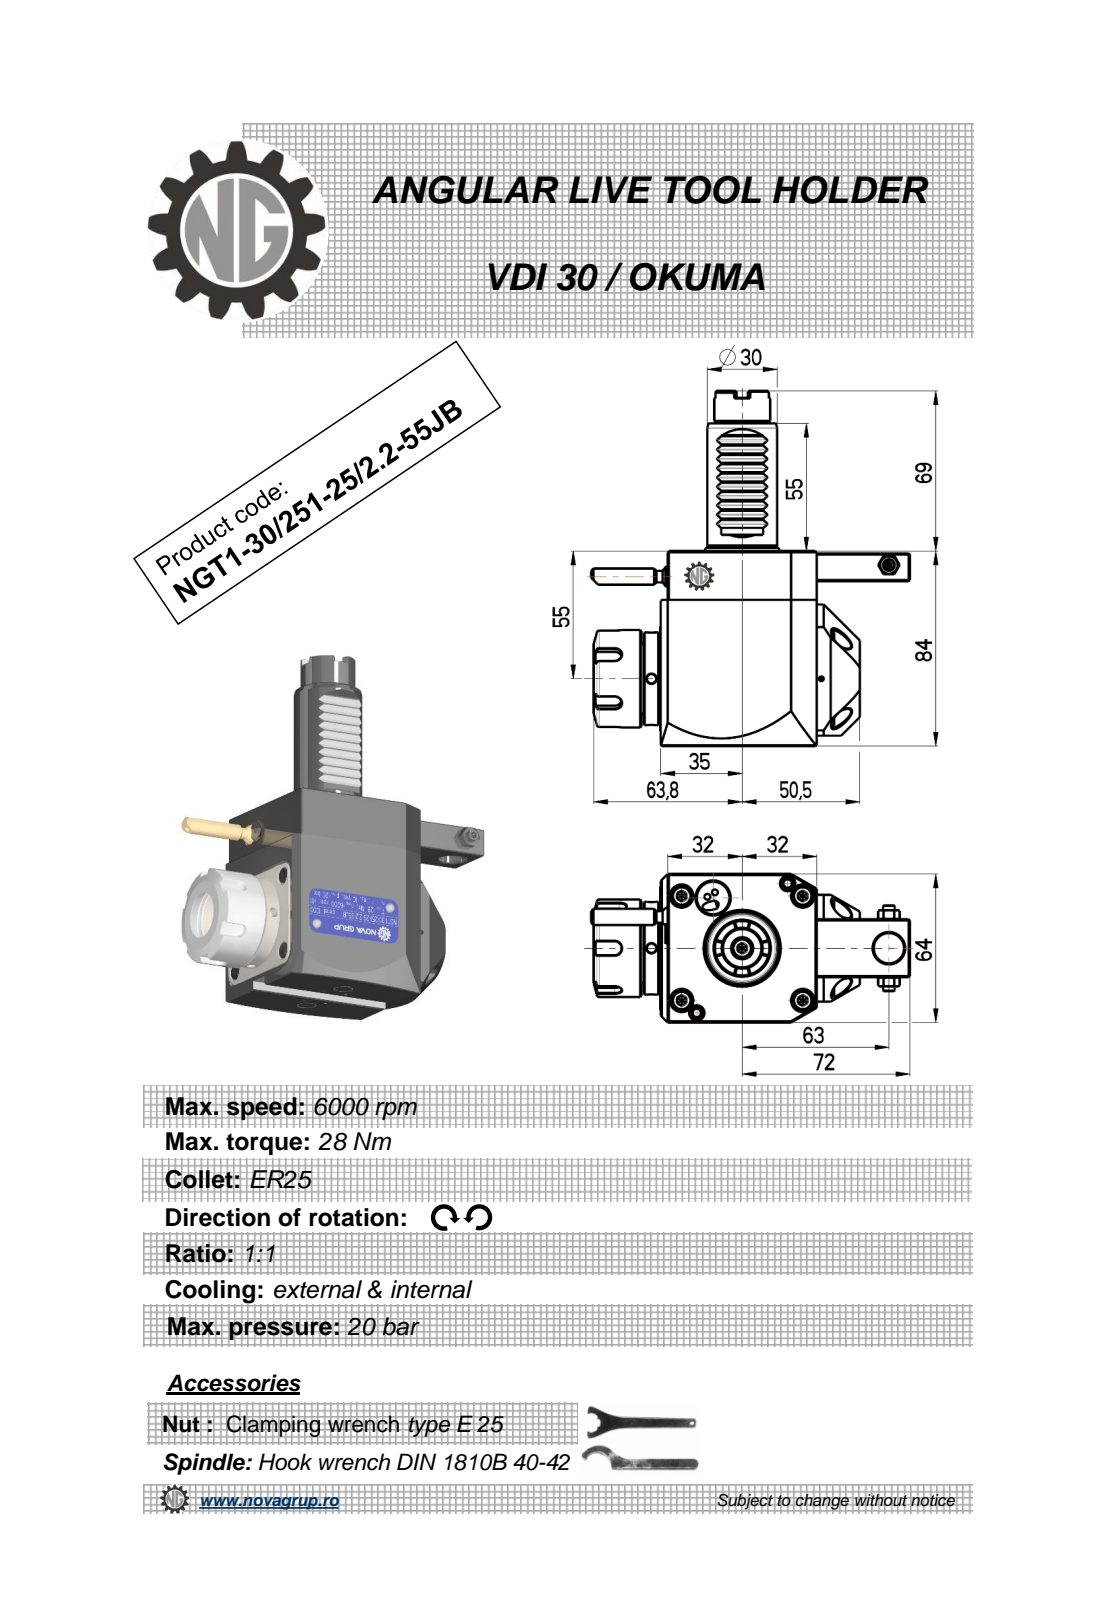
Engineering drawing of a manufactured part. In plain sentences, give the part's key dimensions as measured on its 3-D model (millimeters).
The part is named "NGT1_30_251_25_2_2_55JB". Its 3-D file was written by "PRO/ENGINEER BY PARAMETRIC TECHNOLOGY CORPORATION, 2010280 (CONFIG_CONTROL_DESIGN)". It is 1 solid with 465 faces: 205 planar, 86 cylindrical and 174 other. Overall it measures 153 by 136.88 by 65.6 millimeters. Its volume is 466 000 cubic millimeters and its surface area 49 716 square millimeters. Round holes: 2 of diameter 4, 1 of diameter 2.5, 1 of diameter 3, 1 of diameter 4.2, 1 of diameter 9.5, 1 of diameter 13, 1 of diameter 17, 1 of diameter 20.3. Round bosses or shafts: 2 of diameter 8.96, 2 of diameter 5, 1 of diameter 42, 1 of diameter 40, 1 of diameter 33, 1 of diameter 30, 1 of diameter 24, 1 of diameter 7. Partial cylindrical surfaces (rounded edges, fillets, slot ends): 12 of radius 0.26, 10 of radius 0.3, 5 of radius 3, 2 of radius 160, 1 of radius 32. The main face-to-face distances are 64, 84, 67, 67.2, 3, 3.2, 1, 0.5, 83, 55. The hole center spacings are 14.08, 38.95, 46.02, 48, 63, 101.95, 113.11.
